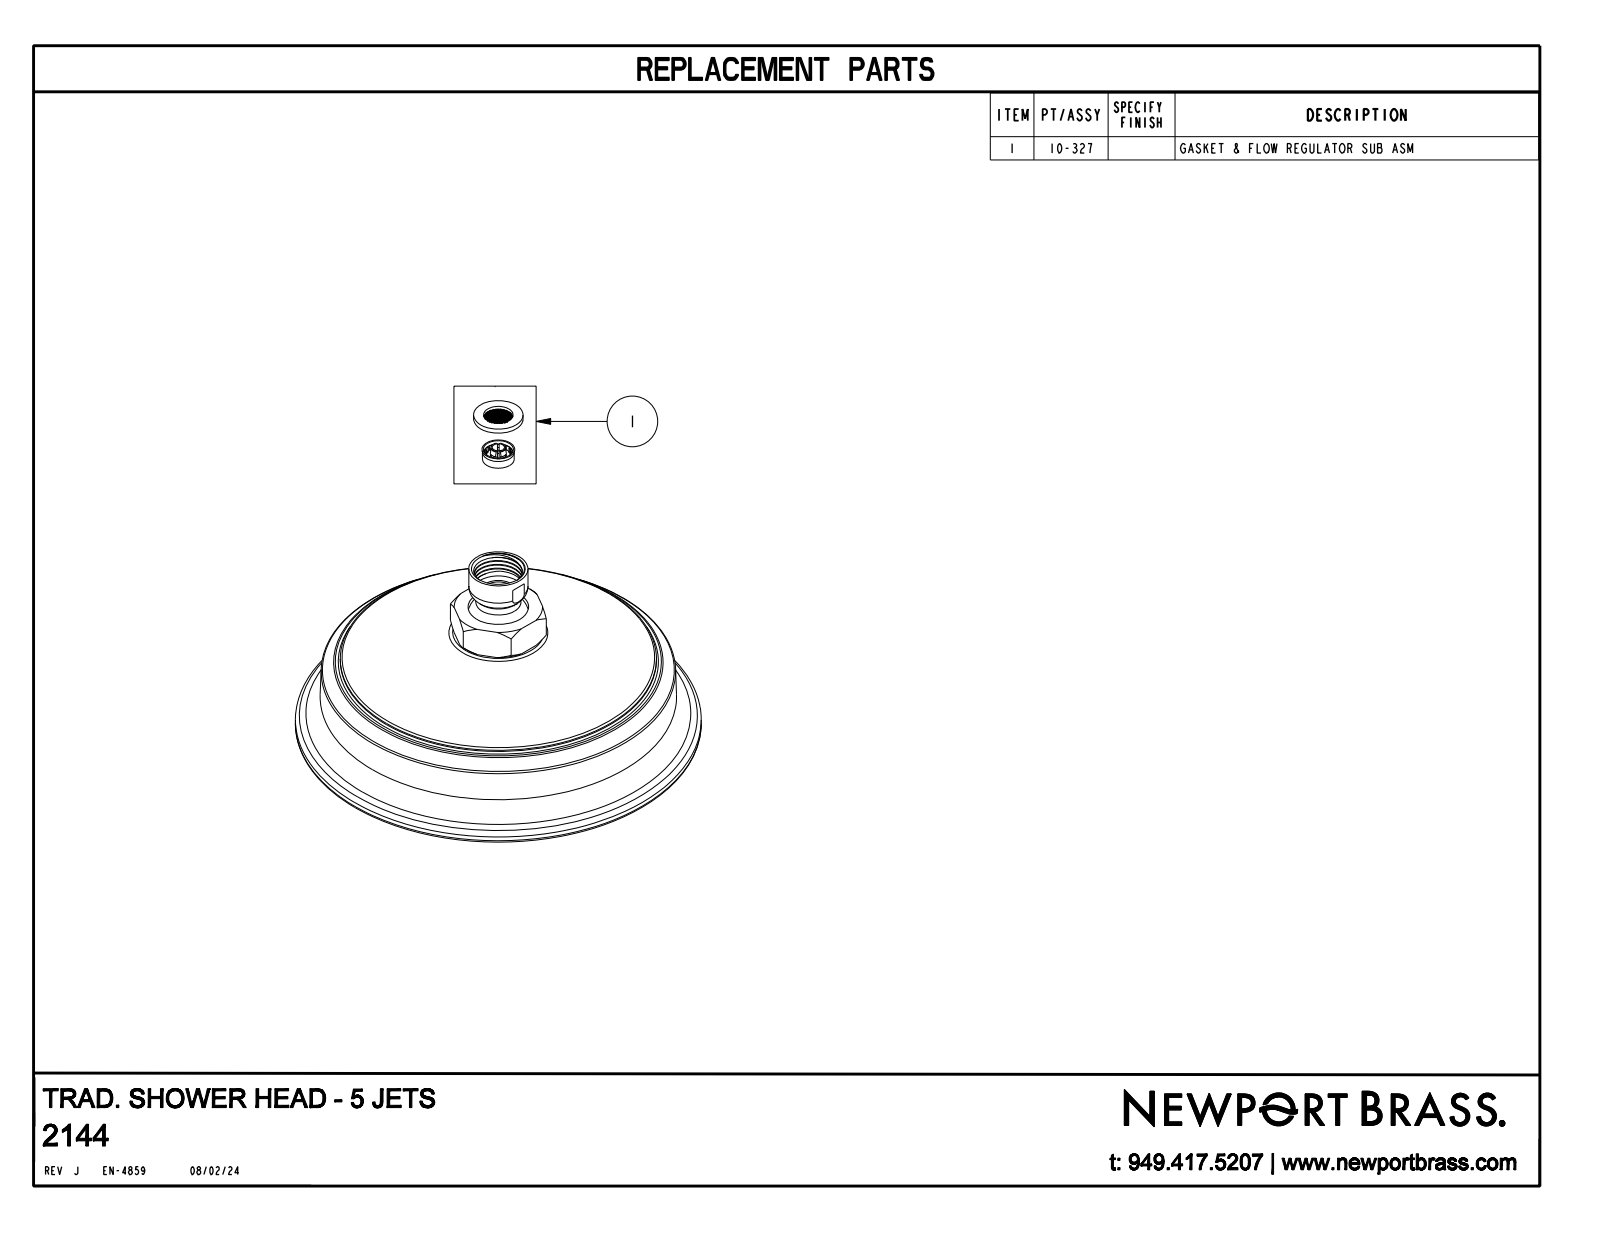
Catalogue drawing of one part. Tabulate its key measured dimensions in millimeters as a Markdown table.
| quantity | value |
| --- | --- |
| part name | 2144 |
| STEP written by | CREO PARAMETRIC BY PTC INC, 2018400 (AUTOMOTIVE_DESIGN) |
| units | millimeters |
| bodies | 1 solid, 1923 faces (254 planar, 508 cylindrical, 1161 other) |
| overall size | 157.5 × 157.5 × 84.4 |
| volume | 599 100 mm³ |
| surface area | 84 060 mm² |
| round holes (diameter × count) | 4.5 × 85, 9 × 3, 25.7 × 1, 30.6 × 1, 42.2 × 1, 44.8 × 1 |
| round bosses / shafts (diameter × count) | 3 × 71, 3 × 15, 157.5 × 1, 122.7 × 1, 44.5 × 1, 42 × 1, 39.6 × 1, 29.7 × 1 |
| partial cylindrical surfaces (radius × count) | 0.5 × 6, 0.8 × 4, 4.2 × 1, 5.3 × 1 |
| main face-to-face distances | 73.8, 48.4, 25.5, 30.6, 17.8, 43.2, 0.7, 3.1, 33.8, 51.5 |
| hole center spacings | 47.8, 36.5, 12.5, 10.9, 24.7, 36.6, 58.2, 67.6 |
